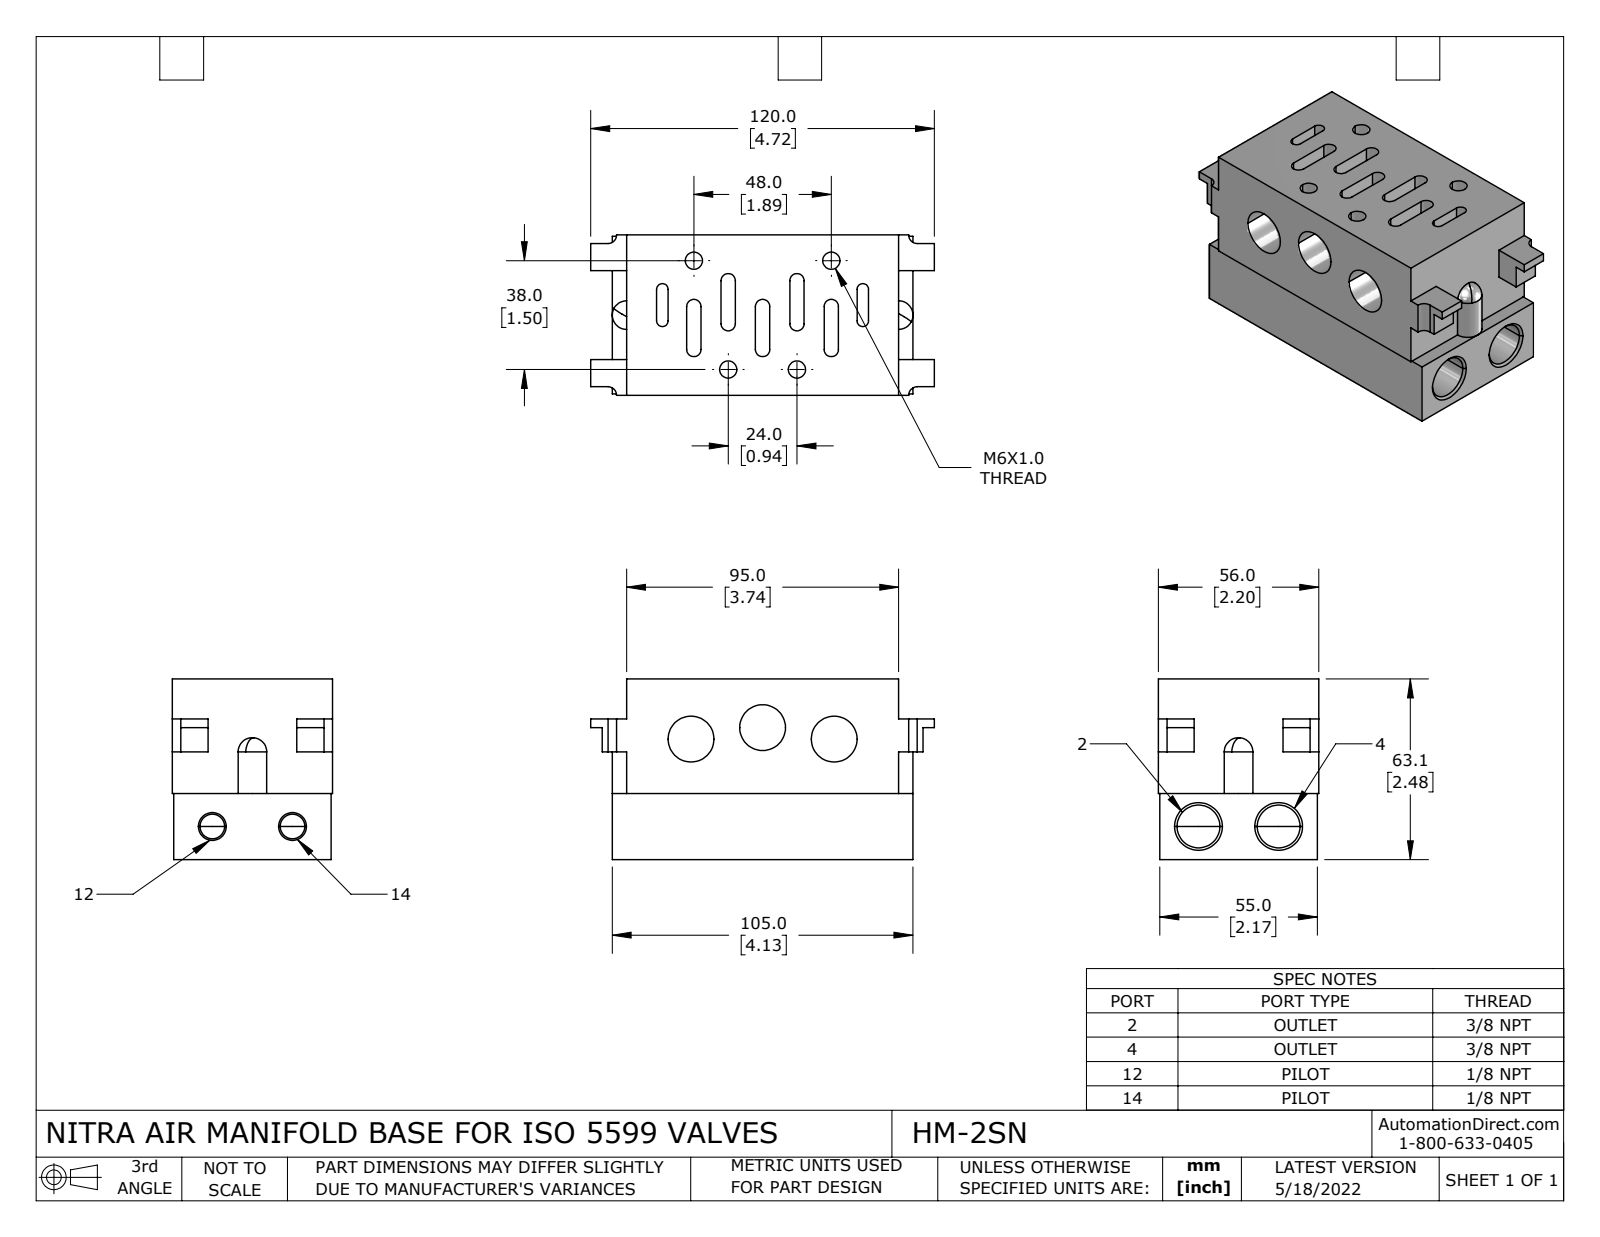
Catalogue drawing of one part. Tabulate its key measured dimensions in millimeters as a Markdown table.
| quantity | value |
| --- | --- |
| part name | HM-2SN |
| STEP written by | SolidWorks 2021 (CONFIG_CONTROL_DESIGN) |
| units | millimeters |
| bodies | 1 solid, 140 faces (72 planar, 48 cylindrical, 20 other) |
| overall size | 120 × 63.1 × 56 |
| volume | 307 182 mm³ |
| surface area | 44 499 mm² |
| round holes (diameter × count) | 6 × 4, 16 × 3, 21 × 3, 8.57 × 2, 14.95 × 2 |
| partial cylindrical surfaces (radius × count) | 2.5 × 10, 2 × 4, 3 × 4, 5 × 2 |
| main face-to-face distances | 0.5, 55.5, 63.1, 5, 56, 55, 100, 95, 12, 3 |
| hole center spacings | 25.32, 39.85, 52.35, 24, 28, 48, 50 |
